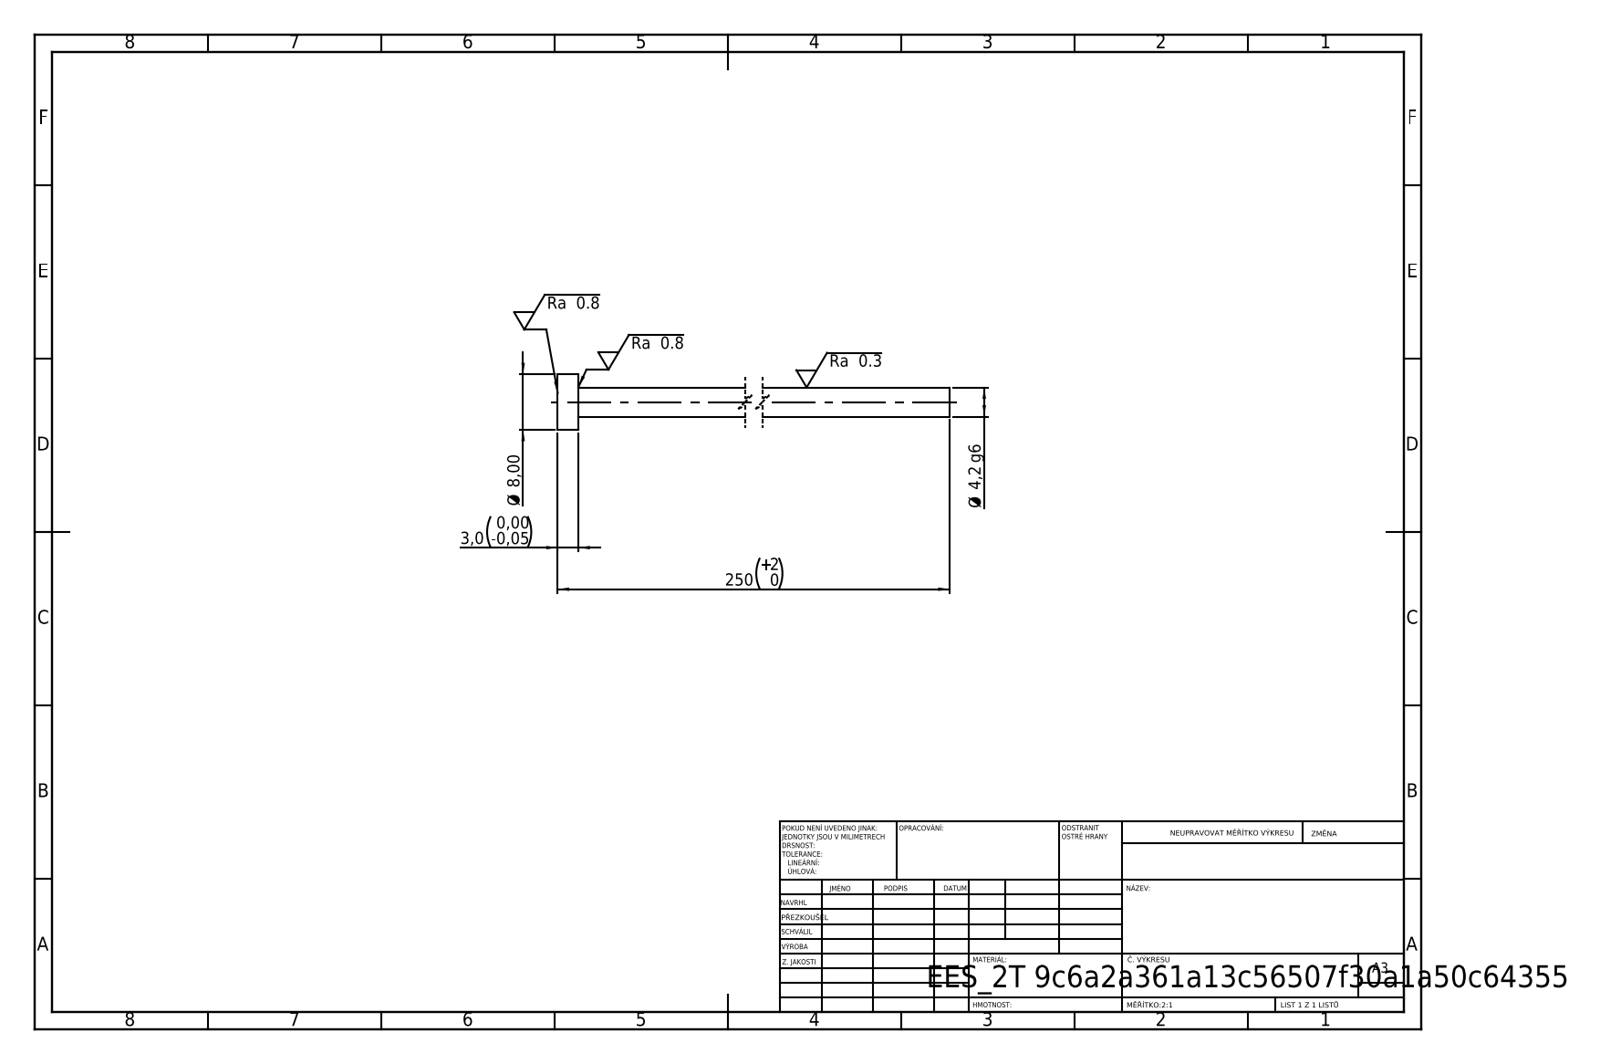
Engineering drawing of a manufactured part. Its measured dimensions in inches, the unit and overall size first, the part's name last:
Units: inches
Overall size (bounding box): 9.843 × 0.315 × 0.315
Round bosses / shafts (diameter × count): ⌀0.315 ×1, ⌀0.165 ×1
Main face-to-face distances: 0.118, 9.843, 9.724
Volume: 0.218 in³ · Surface area: 5.324 in²
Bodies: 1 solid, 7 faces (3 planar, 4 cylindrical, 0 other)
STEP written by: SolidWorks 2019 (CONFIG_CONTROL_DESIGN)
